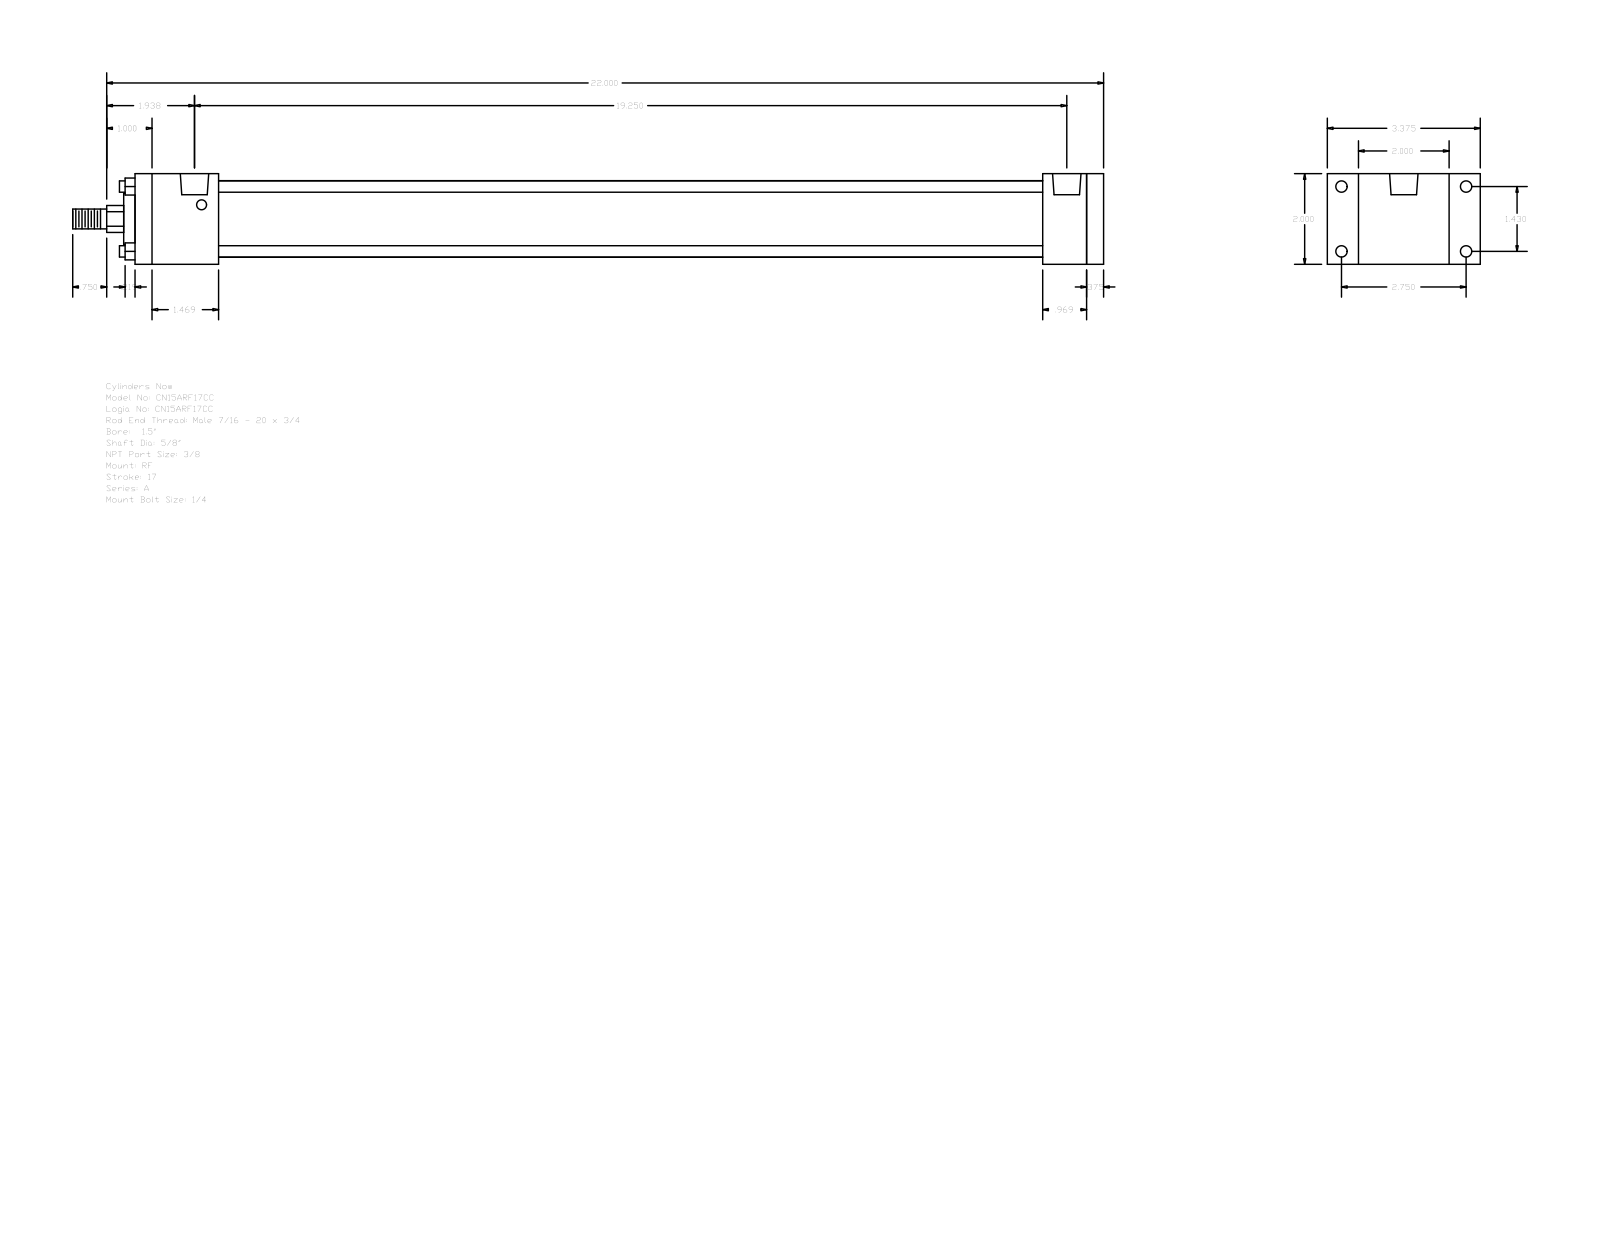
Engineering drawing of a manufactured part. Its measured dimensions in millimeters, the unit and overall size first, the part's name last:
Units: millimetres
Overall size (bounding box): 577.85 × 85.72 × 50.8
Round holes (diameter × count): ⌀5.56 ×4, ⌀6.35 ×4, ⌀15.93 ×2
Round bosses / shafts (diameter × count): ⌀6.35 ×4, ⌀42.93 ×1, ⌀28.57 ×1, ⌀15.88 ×1, ⌀11.11 ×1
Partial cylindrical surfaces — rounded edges, fillets, slot ends (radius × count): R7.54 ×1
Main face-to-face distances: 50.8, 9.53, 542.92, 533.39, 508.79, 24.6, 34.13, 46.83, 461.96, 486.56
Hole centre spacings: 3.97, 36.32, 69.84, 78.72, 481.01, 484.98, 488.95
Bodies: 0 solids, 92 faces (64 planar, 28 cylindrical, 0 other)
Part name (STEP PRODUCT): A_RF__0150_0.625
STEP written by: GSSL Pune (CONFIG_CONTROL_DESIGN)
